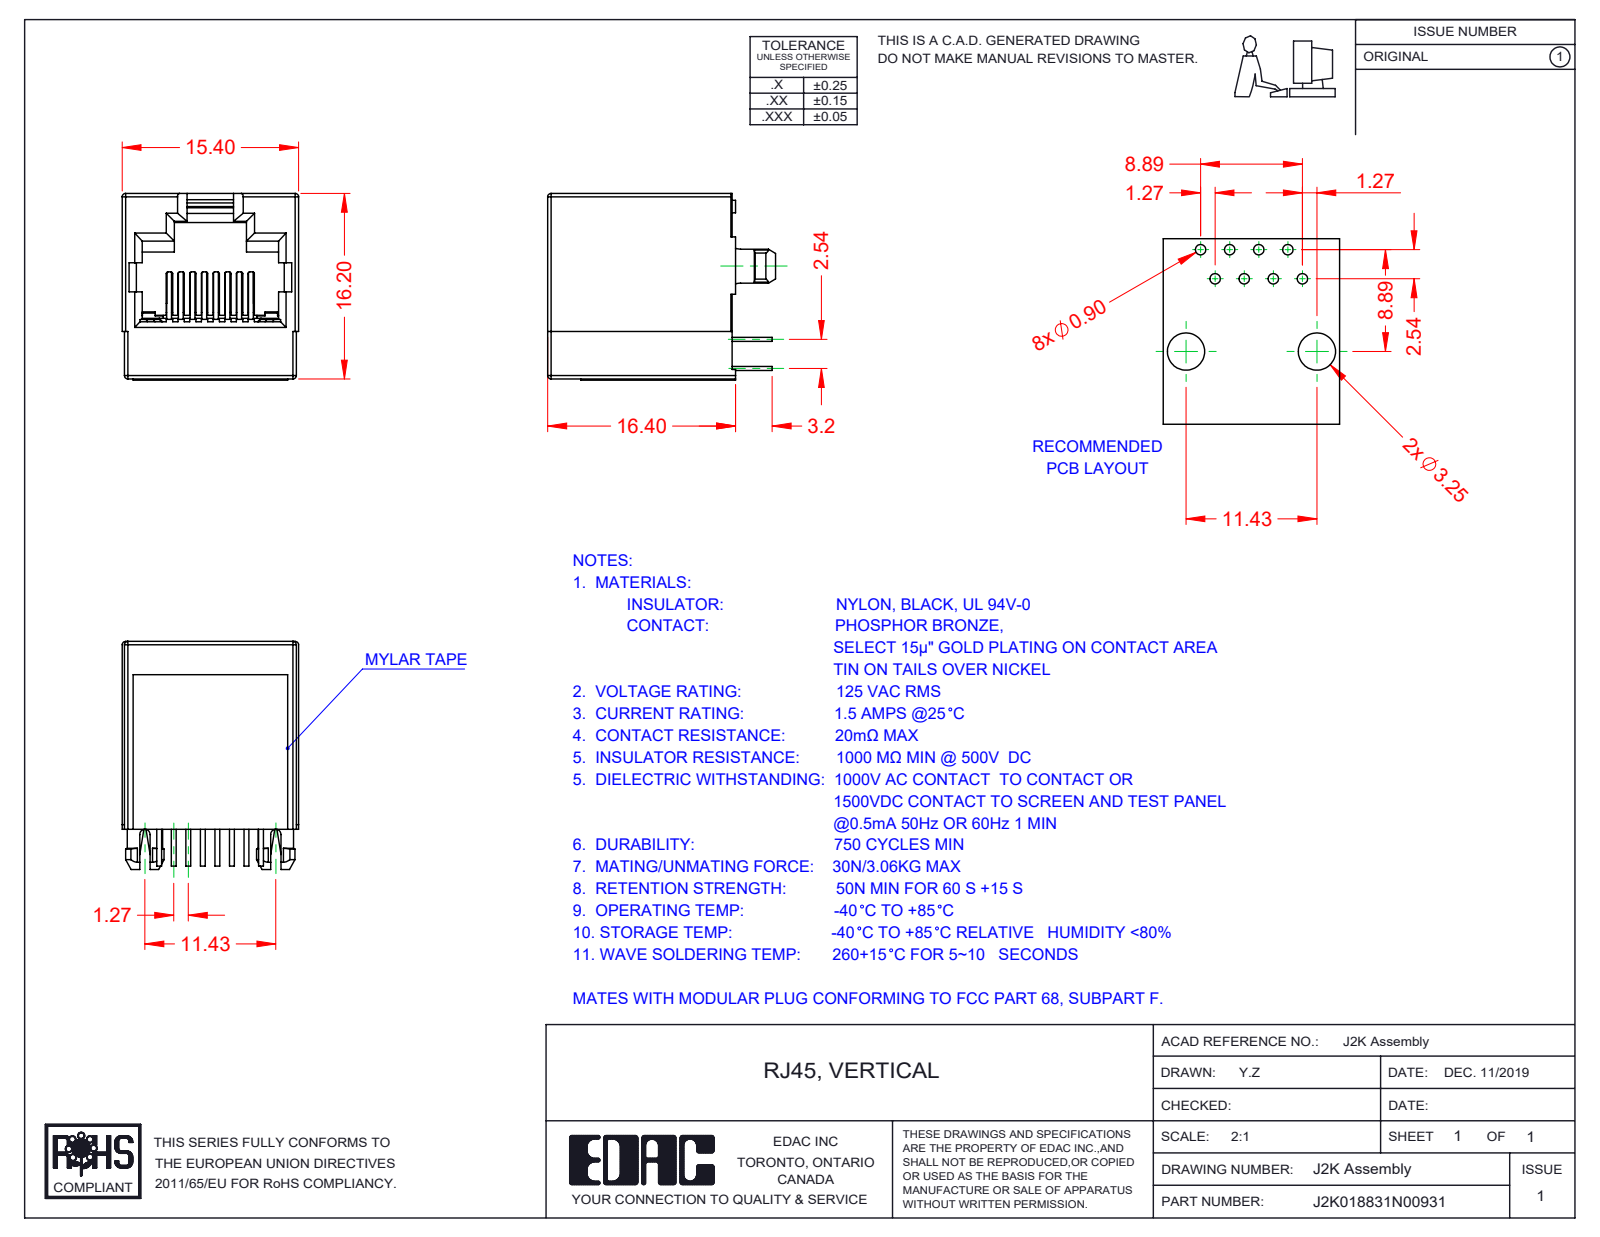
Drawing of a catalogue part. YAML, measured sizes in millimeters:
part_name: "RJ2K018831N00931; 2K Contact Lock; 2K Contacts; 2K Insulator (+1 more)"
step_written_by: "SolidWorks 2016 (CONFIG_CONTROL_DESIGN)"
units: millimeters
bodies: {solids: 11, faces: 729, planar: 592, cylindrical: 113, other: 24}
overall_size: [19.9, 16.3, 15.4]
volume: 2491
surface_area: 4332
round_bosses_or_shafts:
  - {diameter: 3.1, count: 2}
  - {diameter: 1.1, count: 2}
partial_cylinders:
  - {radius: 0.15, count: 16}
  - {radius: 0.3, count: 10}
  - {radius: 0.5, count: 3}
  - {radius: 0.1, count: 2}
  - {radius: 0.2, count: 2}
  - {radius: 0.45, count: 2}
  - {radius: 0.6, count: 2}
  - {radius: 0.95, count: 2}
face_to_face_distances: [16.2, 15.4, 16.3, 14, 1.4, 1.2, 13.8, 15.2, 0.5, 1.3]
